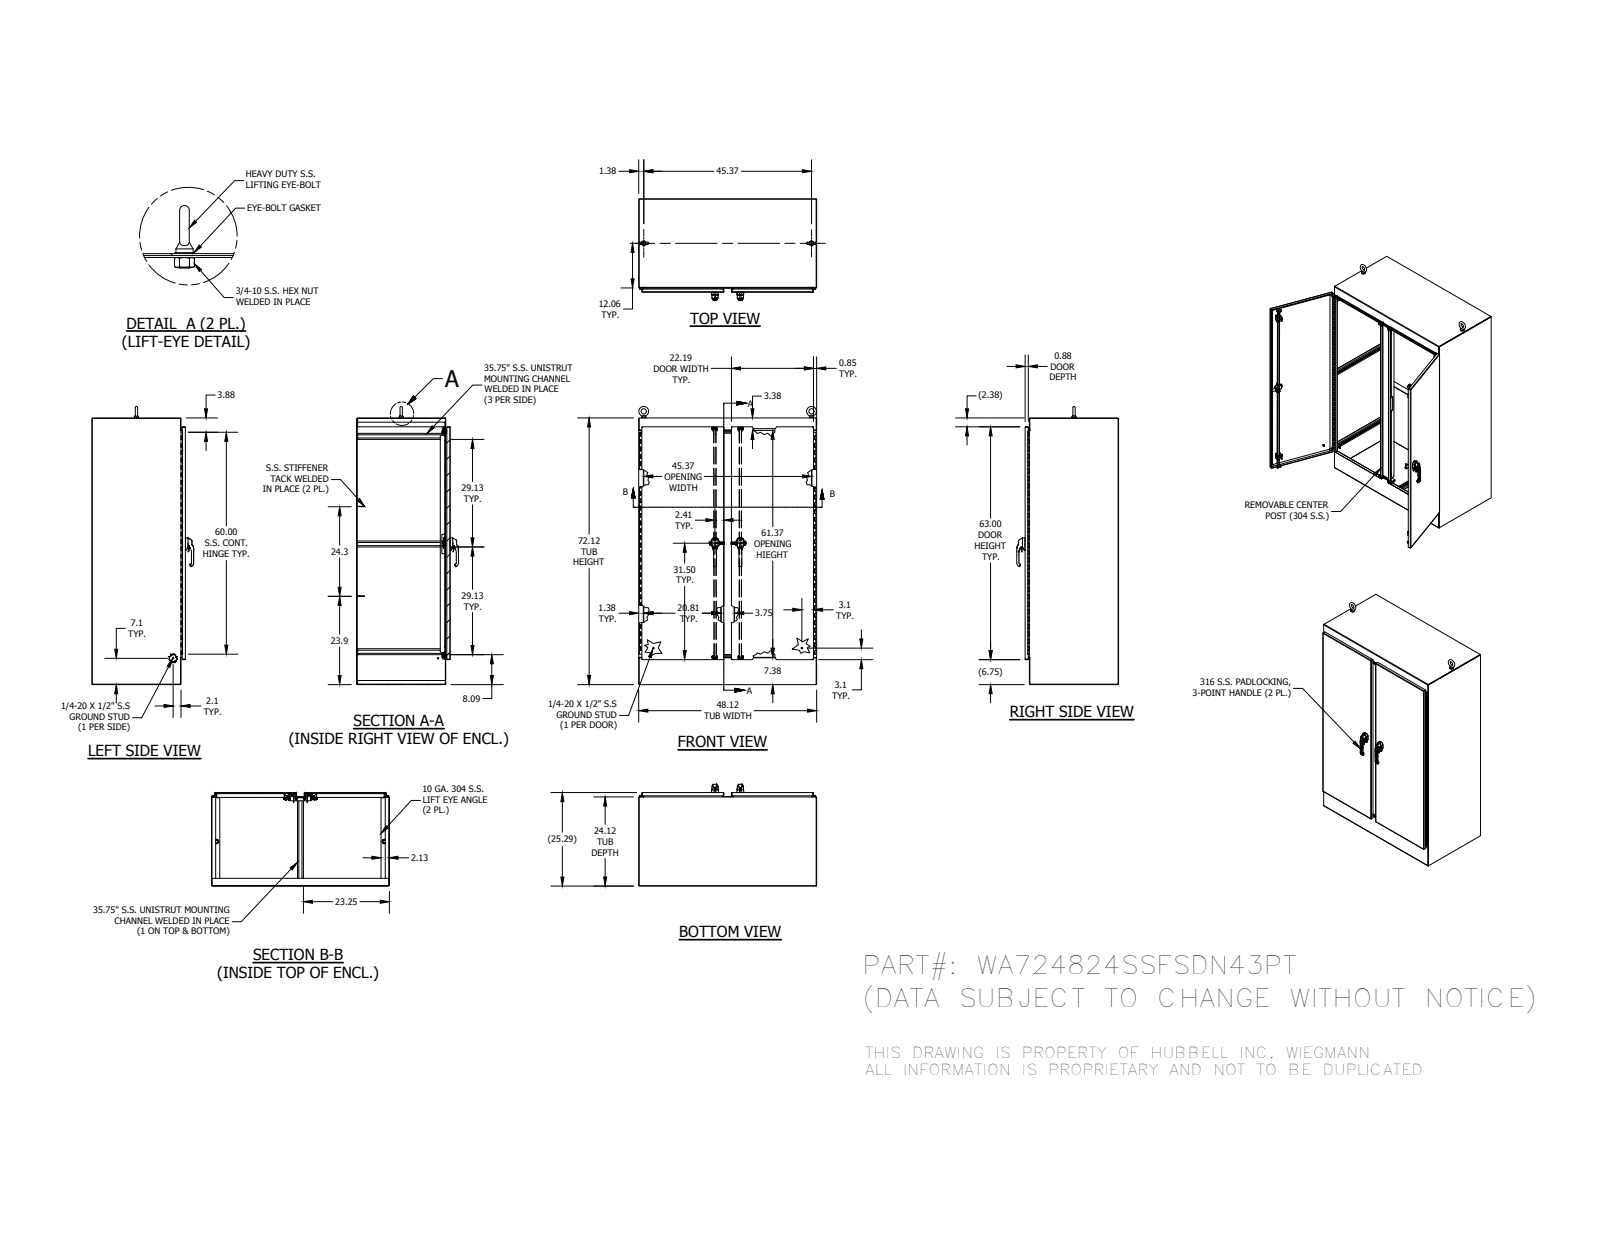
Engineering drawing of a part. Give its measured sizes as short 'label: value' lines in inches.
name: PLASTIC-ROLLER-CAM_AF0_ASM; 3862; 328131L-60; WA48SSFSDN43PTSTFNR (+8 more)
written by: SolidWorks 2014 (AUTOMOTIVE_DESIGN)
unit: in
bodies: 133 solids, 7024 faces (2638 planar, 2690 cylindrical, 1696 other)
size: 75.248 × 48.125 × 27.541
volume: 1 968 in³; area: 32 205 in²
holes: 16× ⌀0.262, 16× ⌀0.375, 8× ⌀0.187, 6× ⌀0.213, 6× ⌀0.281, 5× ⌀0.25, 4× ⌀0.196, 4× ⌀0.241, 4× ⌀0.252, 4× ⌀0.281, 4× ⌀0.315, 4× ⌀0.4
bosses: 7× ⌀0.25, 6× ⌀0.533, 6× ⌀0.236, 5× ⌀1, 4× ⌀0.563, 4× ⌀0.531, 4× ⌀0.5, 4× ⌀0.438
rounds: 352× R0.02, 212× R0.012, 44× R0.019, 44× R0.125, 34× R0.05, 28× R0.079, 24× R0.025, 23× R0.059
face distances: 0.125, 0.125, 48, 25.167, 72, 24, 1.167, 48.125, 47.875, 25.165
hole spacings: 54.49, 55.24, 20, 0.38, 0.38, 6.667, 0.76, 13.333
